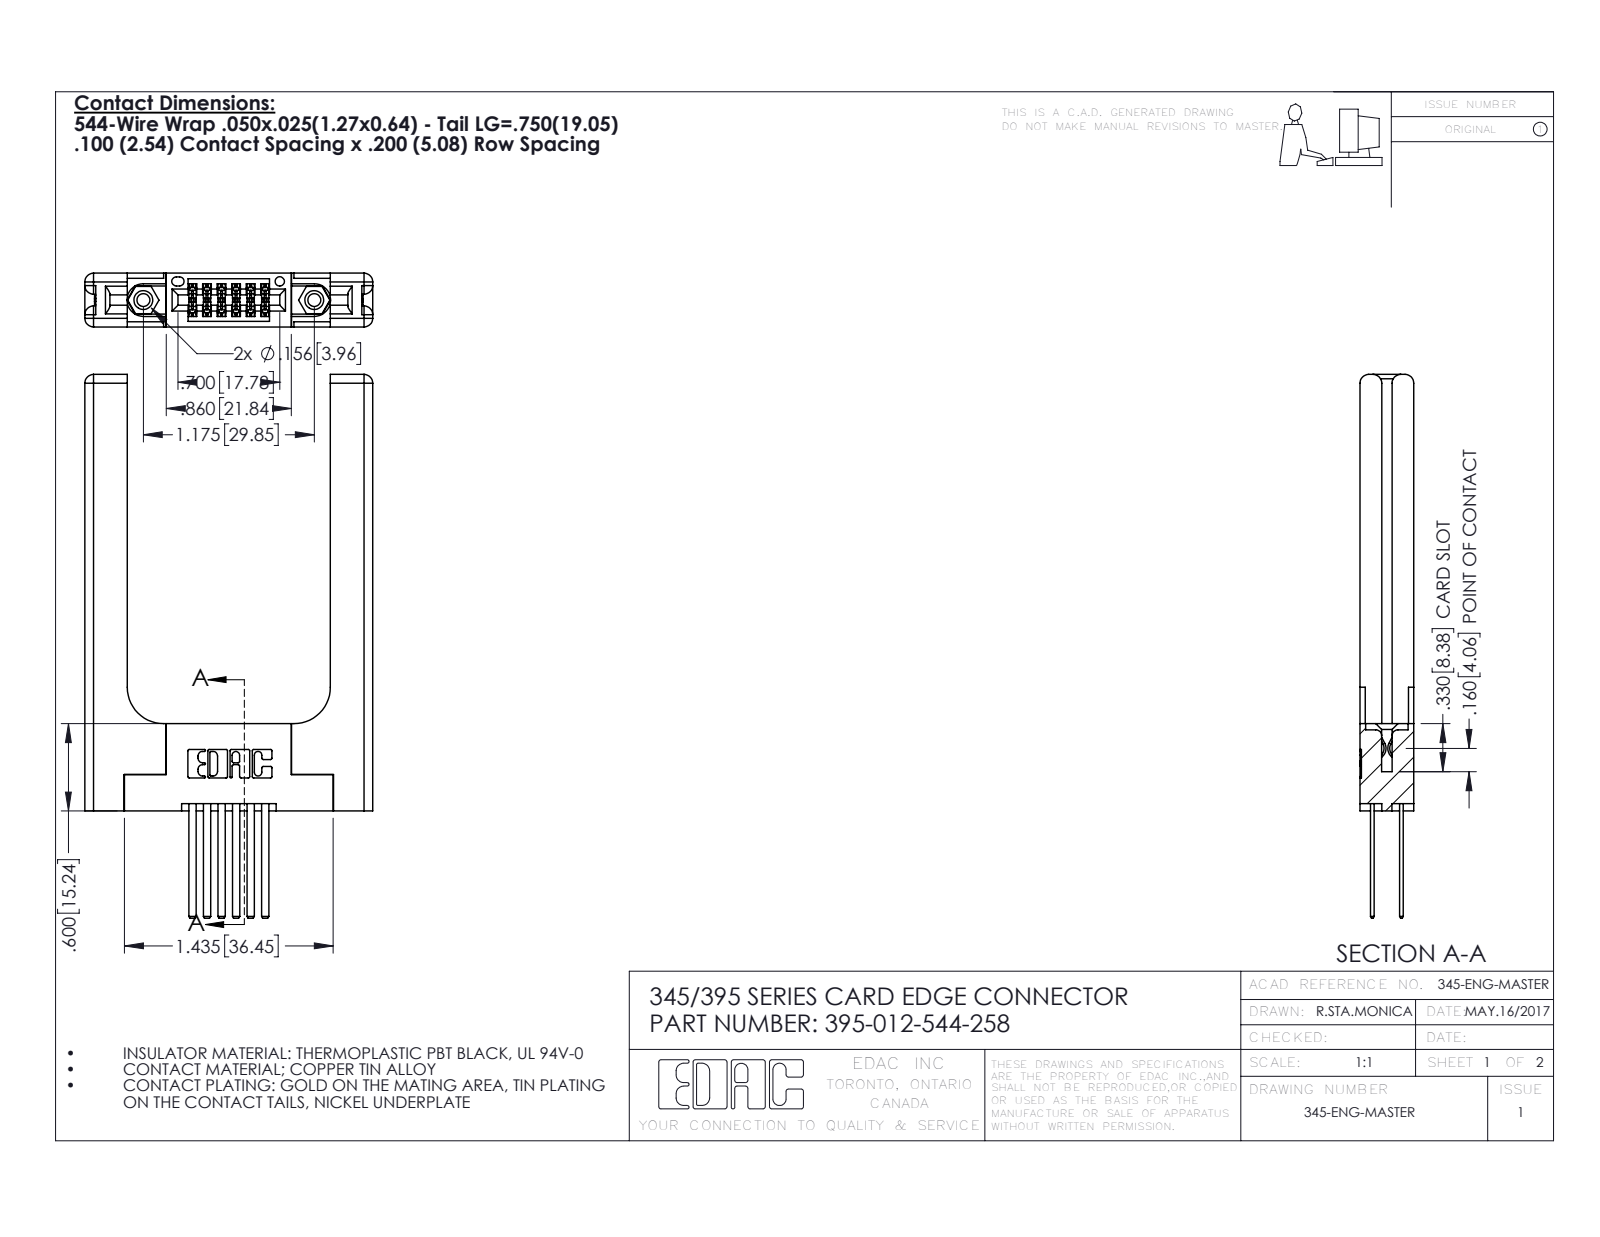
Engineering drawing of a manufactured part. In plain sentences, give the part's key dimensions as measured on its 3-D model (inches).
The part is named "345-250-001_345-250-001-102; 345-220-058_345-220-058; 345 Part_Flush Mounting Lugs - 0.156 Dia-TH; 395-012-544-258 (+1 more)". Its 3-D file was written by "SolidWorks 2016 (CONFIG_CONTROL_DESIGN)". It is 17 solids with 910 faces: 576 planar, 274 cylindrical and 60 other. Overall it measures 3.737 by 1.979 by 0.37 inches. Its volume is 0.805 cubic inches and its surface area 18.33 square inches. Round holes: 2 of diameter 0.089, 2 of diameter 0.125, 2 of diameter 0.156, 1 of diameter 0.064. Round bosses or shafts: 2 of diameter 0.155. Partial cylindrical surfaces (rounded edges, fillets, slot ends): 22 of radius 0.01, 18 of radius 0.006, 16 of radius 0.06, 6 of radius 0.007, 6 of radius 0.031, 3 of radius 0.026, 2 of radius 0.014, 2 of radius 0.019. The main face-to-face distances are 0.37, 0.072, 0.077, 0.148, 0.15, 0.298, 0.22, 0.2, 0.098, 0.272. The hole center spacings are 0.27, 0.946, 1.175.
